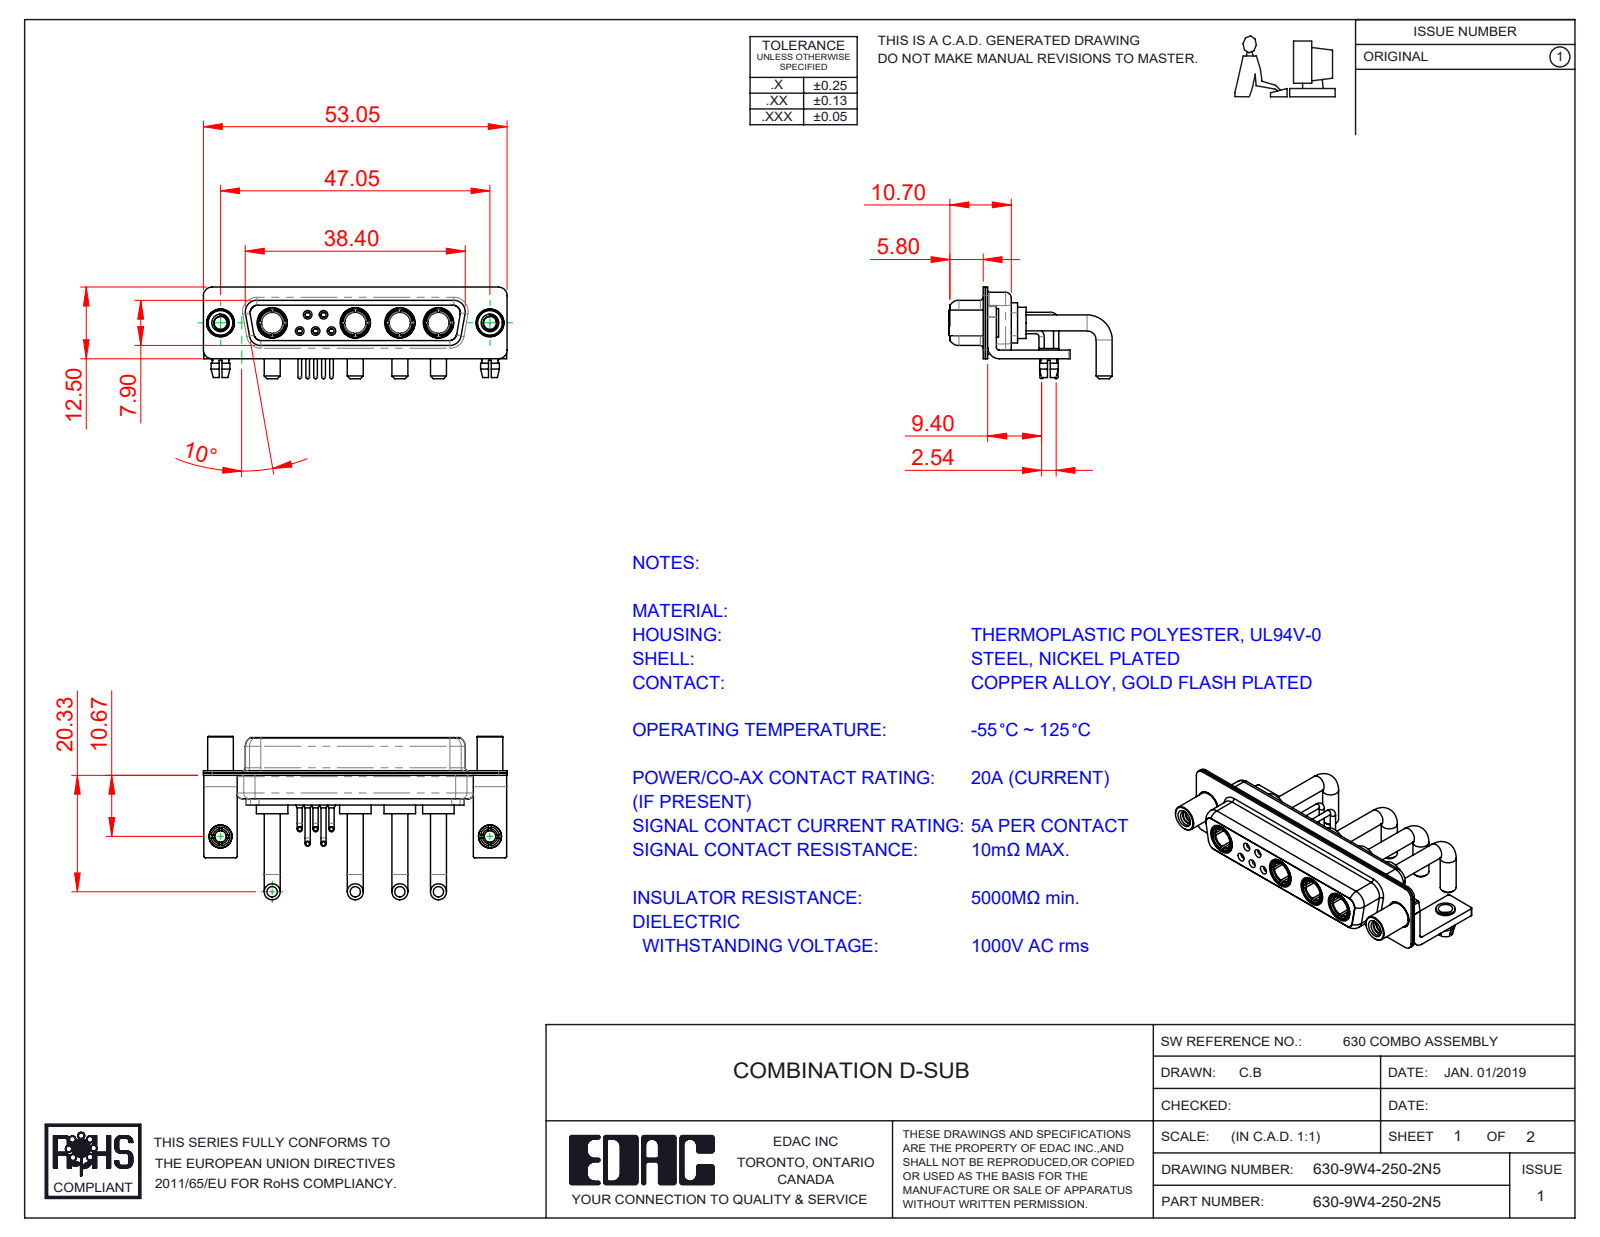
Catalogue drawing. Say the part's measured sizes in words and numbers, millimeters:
The part is named "630Combo Shell Front_25 Contacts; 630Combo Stabilizer Bracket; Power Socket_Ext 20A RA; 630Combo Board Lock (+6 more)". Its 3-D file was written by "SolidWorks 2020 (CONFIG_CONTROL_DESIGN)". It is 22 solids with 1036 faces: 328 planar, 444 cylindrical and 264 other. Overall it measures 53.05 by 28.53 by 16 millimeters. Its volume is 4 632 cubic millimeters and its surface area 10 221 square millimeters. Round holes: 7 of diameter 2, 6 of diameter 4.85, 5 of diameter 0.9, 5 of diameter 1.1, 5 of diameter 1.5, 4 of diameter 3.7, 4 of diameter 5.3, 3 of diameter 1.6, 2 of diameter 1.7, 2 of diameter 2.26, 2 of diameter 2.5, 2 of diameter 3.2. Round bosses or shafts: 8 of diameter 2.8, 5 of diameter 0.9, 5 of diameter 0.65, 4 of diameter 5.5, 4 of diameter 5.2, 4 of diameter 4.96, 4 of diameter 4.75, 4 of diameter 3.75. Partial cylindrical surfaces (rounded edges, fillets, slot ends): 16 of radius 0.25, 16 of radius 1.5, 13 of radius 2, 8 of radius 1.35, 8 of radius 1.6, 5 of radius 0.5, 4 of radius 0.6, 4 of radius 0.65. The main face-to-face distances are 0.4, 0.45, 1.4, 8.45, 1.8, 0.8, 8.9, 1.5, 7.05, 6.2. The hole center spacings are 3.16, 2.77, 47.05, 4.4, 5.02, 5.03, 5.04, 5.54.
